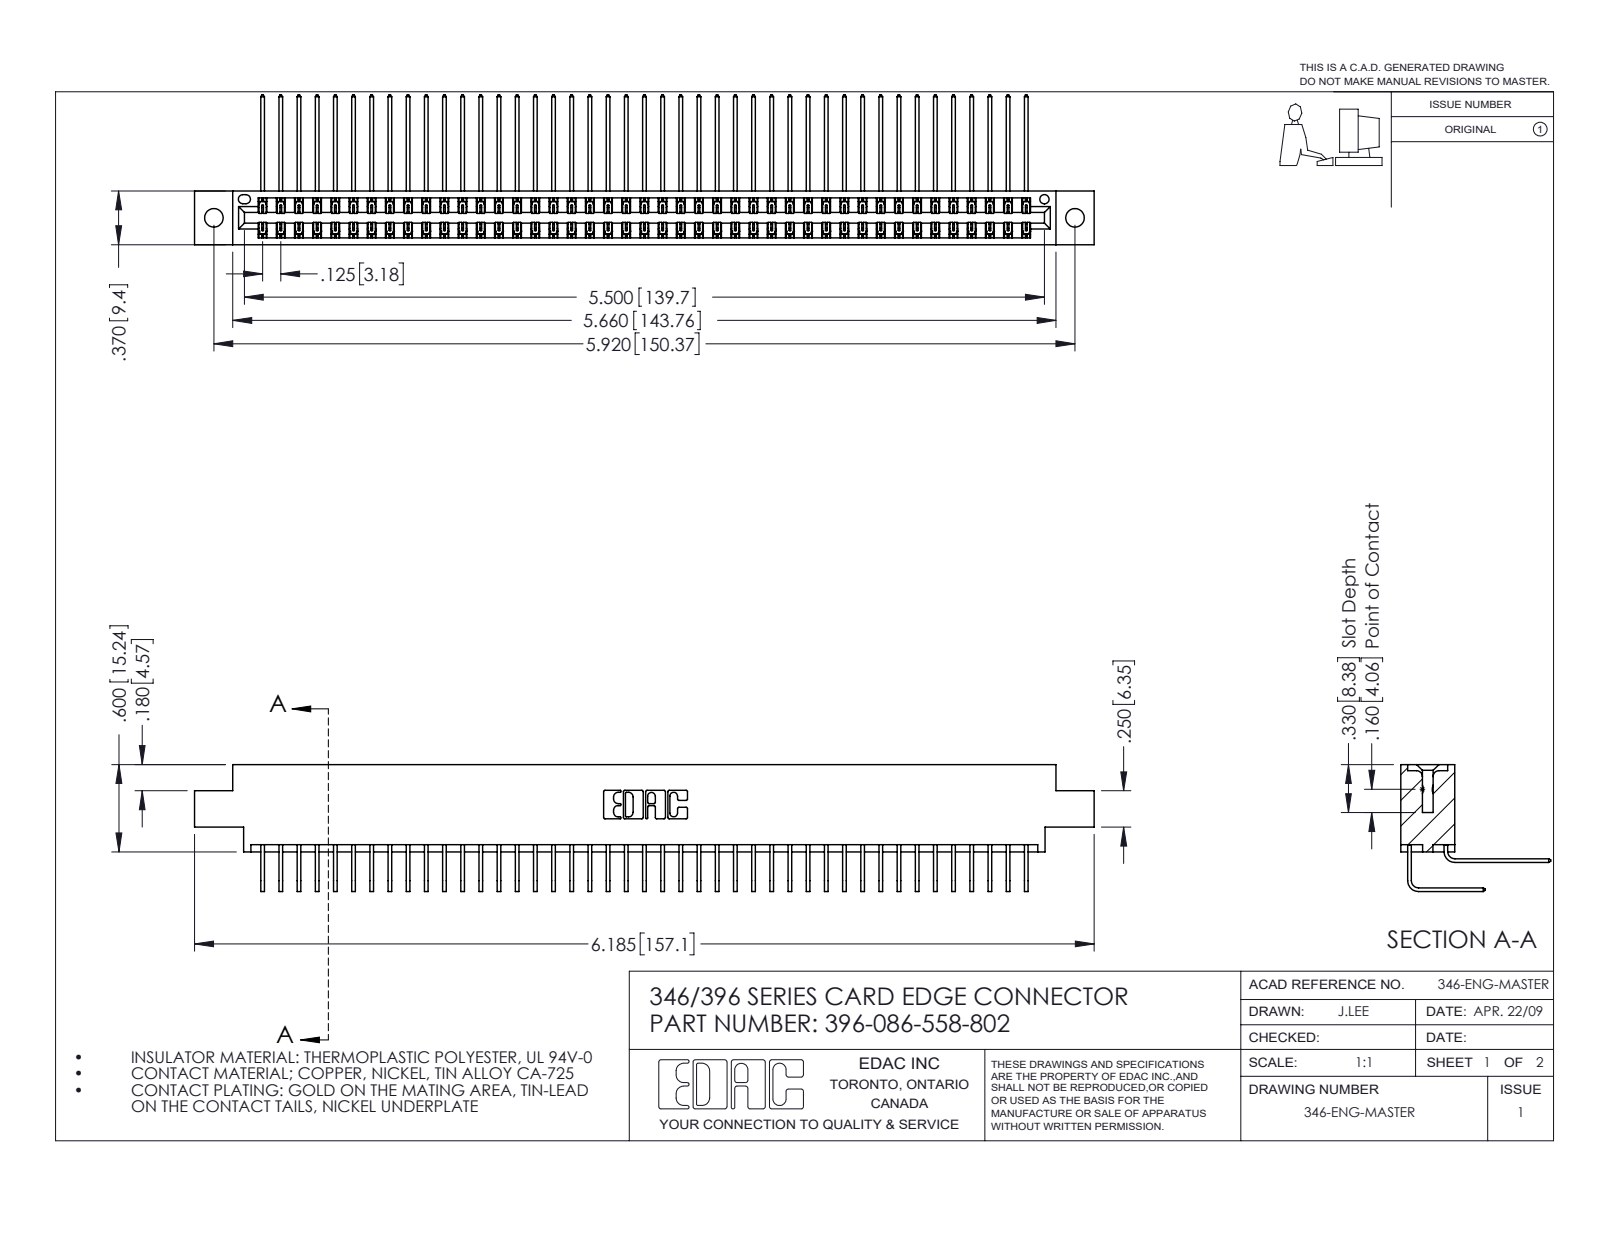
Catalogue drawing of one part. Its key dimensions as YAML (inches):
part_name: "396-086-558-802; 345-292-001_558 Tail - 2; 346 Part_0.170 Offset - 0.128 Dia; 345-292-001_558 559 Tail - 1"
step_written_by: "SolidWorks 2016 (CONFIG_CONTROL_DESIGN)"
units: inches
bodies: {solids: 87, faces: 4770, planar: 3262, cylindrical: 1508, other: 0}
overall_size: [6.185, 1.03, 0.873]
volume: 0.954
surface_area: 36.88
round_holes:
  - {diameter: 0.128, count: 2}
  - {diameter: 0.064, count: 1}
partial_cylinders:
  - {radius: 0.006, count: 129}
  - {radius: 0.01, count: 22}
  - {radius: 0.007, count: 6}
  - {radius: 0.031, count: 6}
  - {radius: 0.026, count: 3}
  - {radius: 0.014, count: 2}
  - {radius: 0.022, count: 2}
  - {radius: 0.024, count: 2}
face_to_face_distances: [0.322, 0.048, 0.025, 0.37, 0.25, 0.298, 0.072, 0.275, 0.148, 0.222]
hole_center_spacings: [0.246, 5.711, 5.92]
